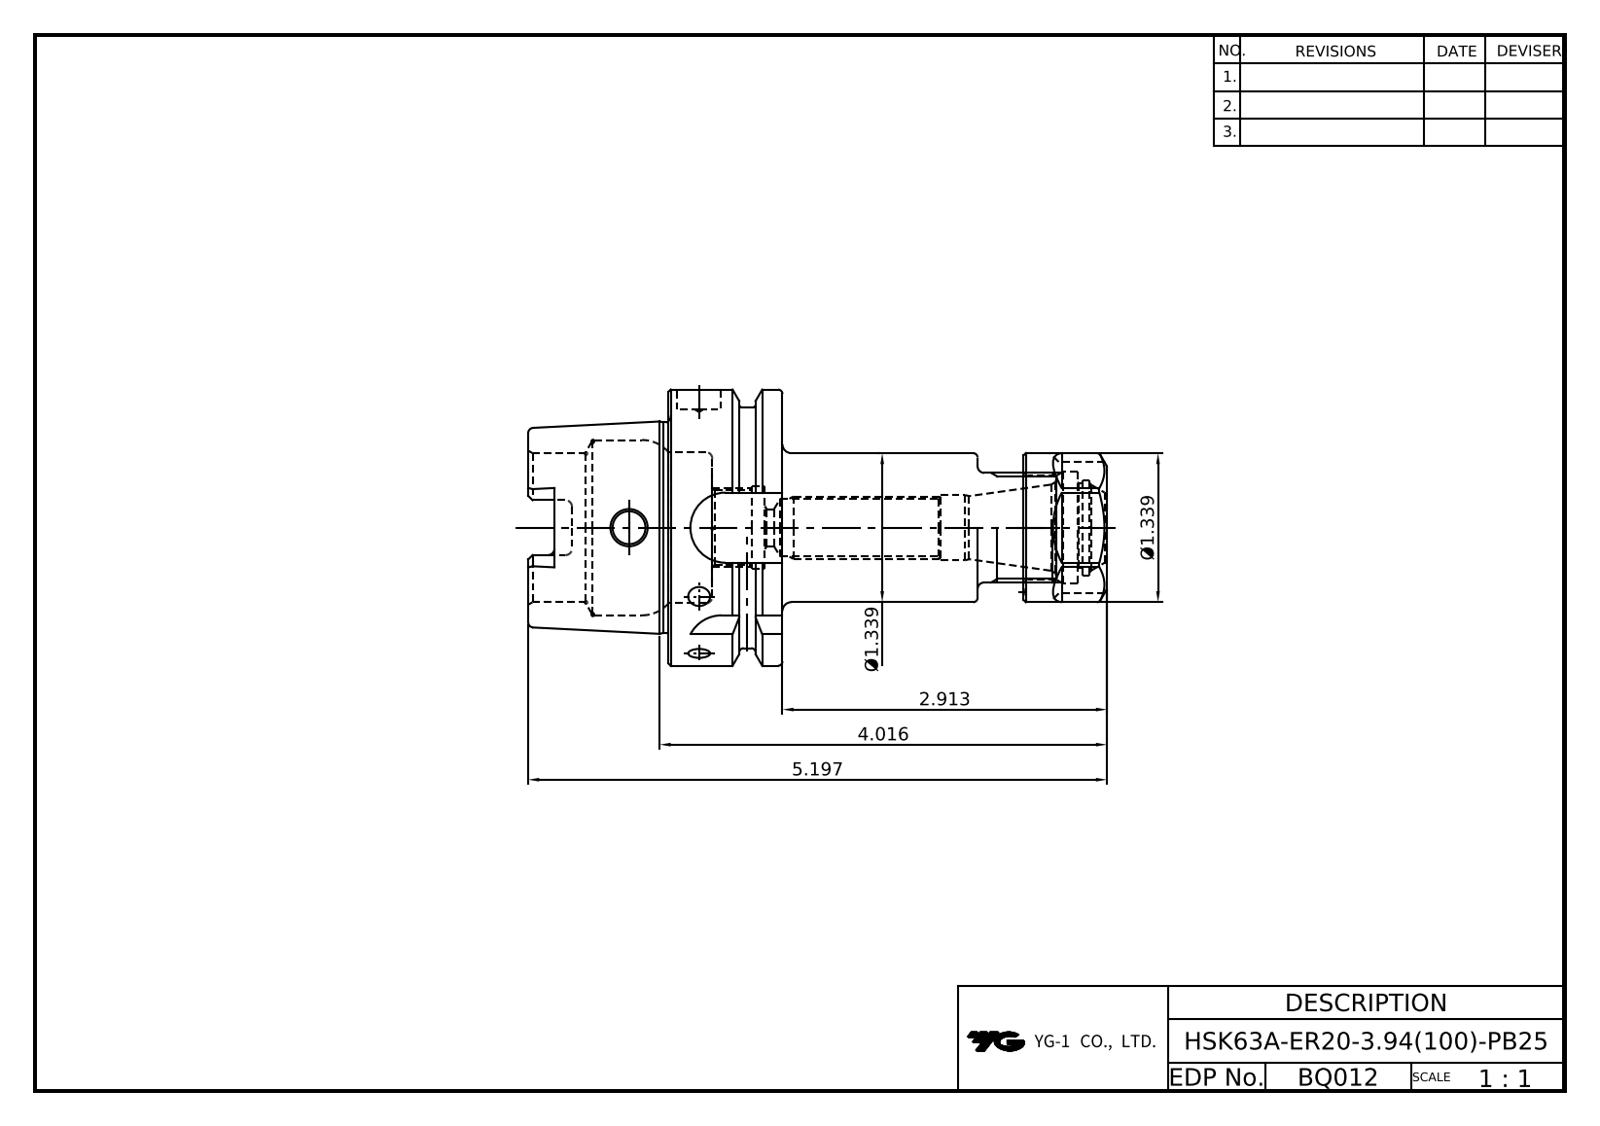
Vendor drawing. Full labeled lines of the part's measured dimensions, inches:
Part name (STEP PRODUCT): HSK63A-ER20-100; LO-HSK63A-ER20-100; ER20NUT
STEP written by: Autodesk Inventor 2022 (AUTOMOTIVE_DESIGN)
Units: inches
Bodies: 2 solids, 149 faces (61 planar, 41 cylindrical, 47 other)
Overall size (bounding box): 5.197 × 2.48 × 2.48
Volume: 7.849 in³ · Surface area: 56.34 in²
Round holes (diameter × count): ⌀0.295 ×1, ⌀0.331 ×1, ⌀0.394 ×1, ⌀0.495 ×1, ⌀0.587 ×1, ⌀0.63 ×1, ⌀0.666 ×1, ⌀0.724 ×1, ⌀0.748 ×1, ⌀0.857 ×1, ⌀0.925 ×1, ⌀1.004 ×1
Round bosses / shafts (diameter × count): ⌀2.48 ×1, ⌀2.165 ×1, ⌀1.891 ×1, ⌀0.984 ×1
Partial cylindrical surfaces — rounded edges, fillets, slot ends (radius × count): R0.059 ×6, R0.113 ×4, R0.315 ×4
Main face-to-face distances: 1.024, 0.394, 0.63, 3.543, 2.913, 1.181, 1.26, 3.937, 0.453, 0.748
